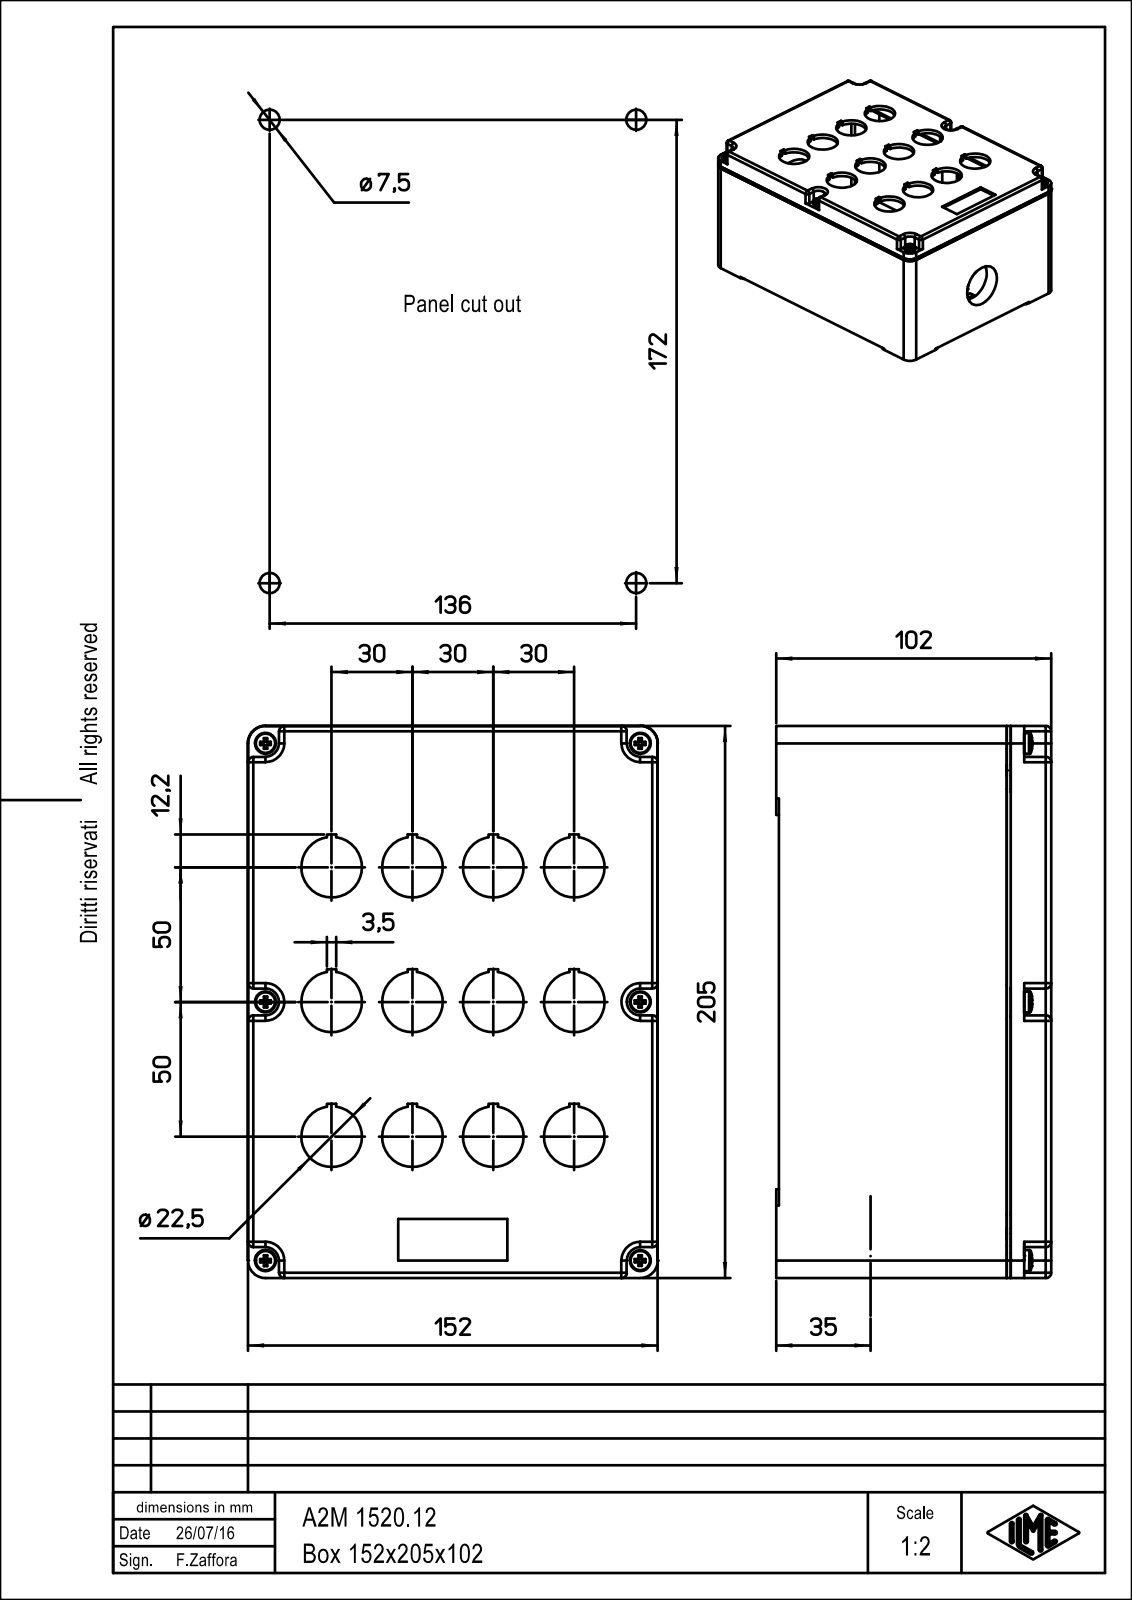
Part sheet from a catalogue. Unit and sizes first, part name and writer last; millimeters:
Units: millimetres
Overall size (bounding box): 205 × 152 × 102
Round holes (diameter × count): ⌀22.5 ×12, ⌀3.3 ×8, ⌀7.5 ×4, ⌀10.6 ×4, ⌀5.8 ×2, ⌀32 ×1
Round bosses / shafts (diameter × count): ⌀7.8 ×6, ⌀4 ×6, ⌀6.2 ×2, ⌀6 ×2, ⌀7 ×1, ⌀3.5 ×1
Partial cylindrical surfaces — rounded edges, fillets, slot ends (radius × count): R2 ×23, R0.33 ×22, R6 ×12, R8 ×10, R5 ×6, R0.27 ×4, R0.27 ×4, R6.5 ×4
Main face-to-face distances: 3, 98, 101, 95, 4.38, 4.37, 152, 205, 13.5, 81.5
Hole centre spacings: 58.31, 30, 50, 78.1, 60, 104.4, 10.11, 86.01
Volume: 558 733 mm³ · Surface area: 282 724 mm²
Bodies: 2 solids, 1126 faces (864 planar, 204 cylindrical, 58 other)
Part name (STEP PRODUCT): BOX; COVER; A2M_1520.12
STEP written by: PTC Creo Elements/Direct Modeling 19.0B 21-Mar-2015 (C) Parametric Technology GmbH (AUTOMOTIVE_DESIGN)
